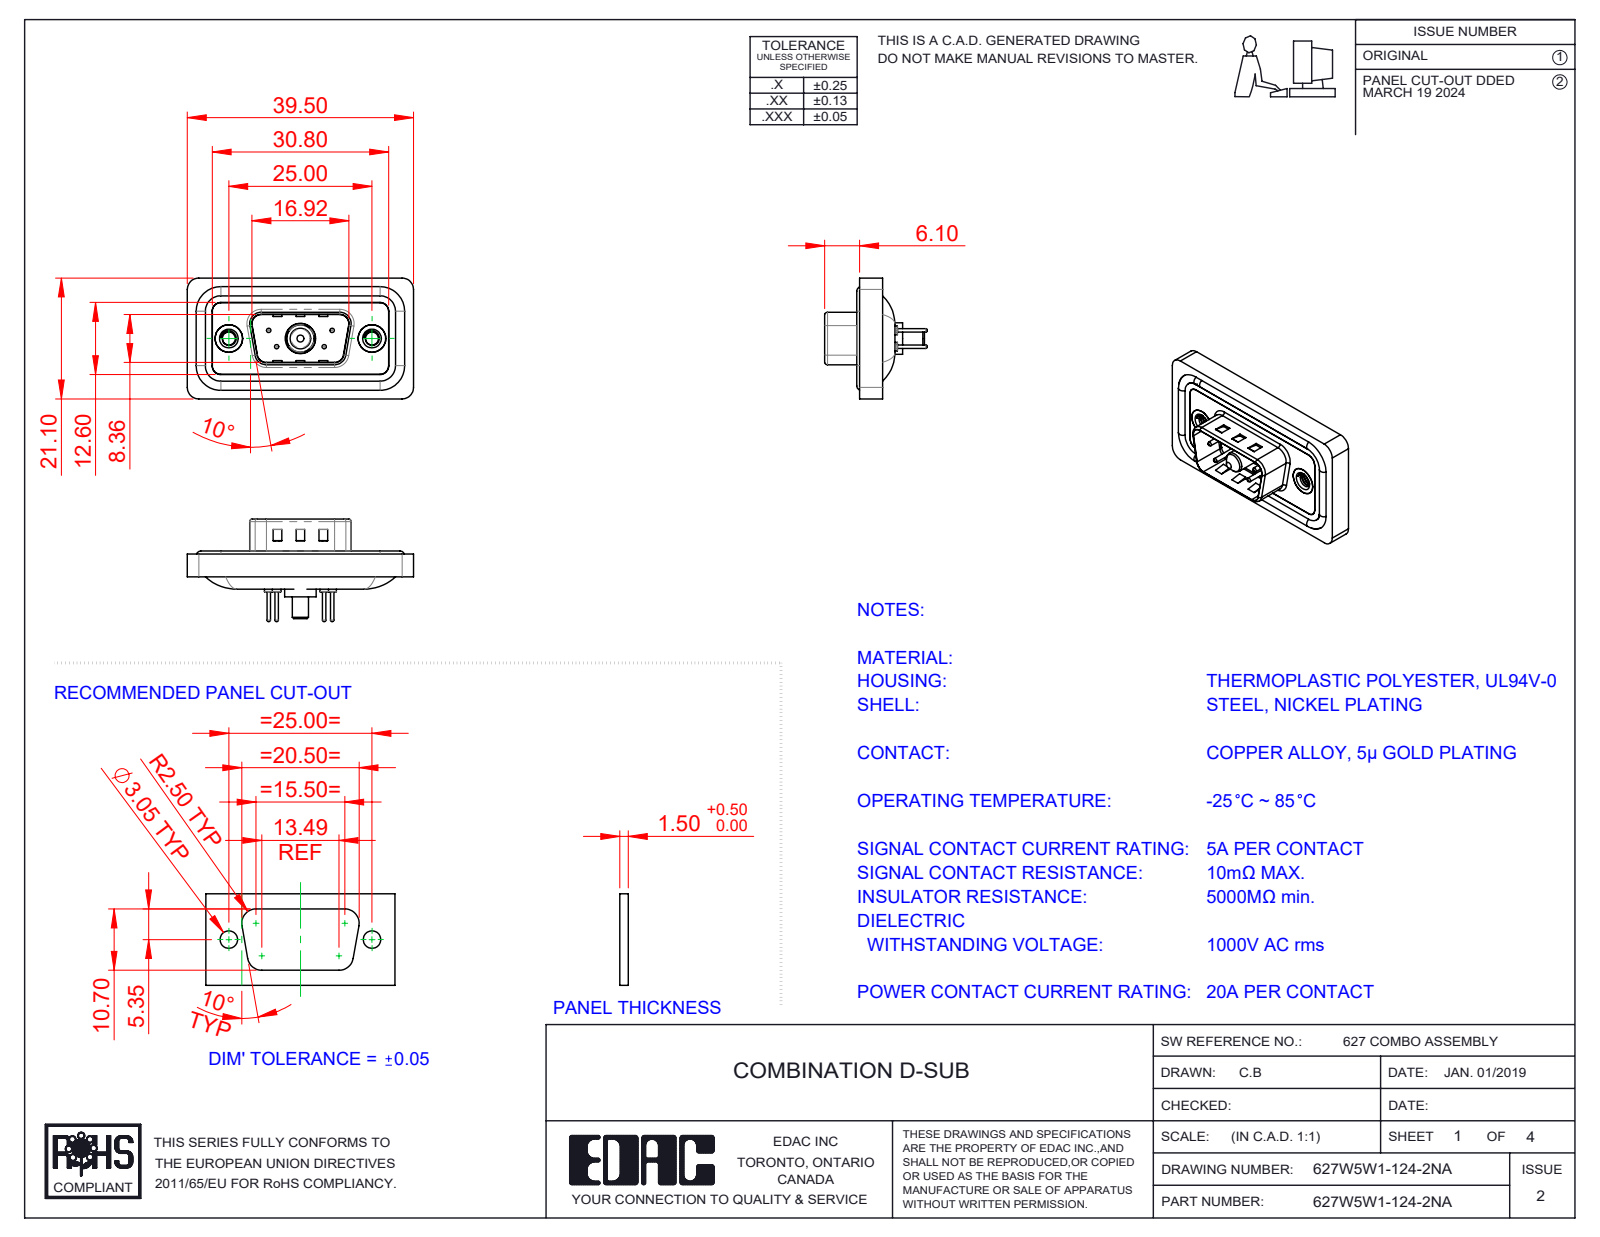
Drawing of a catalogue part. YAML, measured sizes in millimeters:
part_name: "627W5W1-124-2NA; 627Combo Contact Row 2_24; 627Combo Waterproof Housing_09 Contacts; 627Combo Threaded Rivet_A (+5 more)"
step_written_by: "SolidWorks 2023 (CONFIG_CONTROL_DESIGN)"
units: millimeters
bodies: {solids: 13, faces: 596, planar: 183, cylindrical: 257, other: 156}
overall_size: [39.5, 21.1, 17.9]
volume: 4389
surface_area: 6939
round_holes:
  - {diameter: 0.75, count: 4}
  - {diameter: 1.6, count: 4}
  - {diameter: 2, count: 4}
  - {diameter: 2.26, count: 2}
  - {diameter: 4, count: 2}
  - {diameter: 4.8, count: 2}
  - {diameter: 5, count: 2}
  - {diameter: 4.85, count: 1}
  - {diameter: 5.3, count: 1}
round_bosses_or_shafts:
  - {diameter: 1.6, count: 4}
  - {diameter: 1.5, count: 4}
  - {diameter: 0.6, count: 4}
  - {diameter: 4.9, count: 2}
  - {diameter: 5.5, count: 1}
  - {diameter: 5.2, count: 1}
  - {diameter: 4.75, count: 1}
  - {diameter: 3.75, count: 1}
partial_cylinders:
  - {radius: 1.5, count: 22}
  - {radius: 2, count: 18}
  - {radius: 0.5, count: 8}
  - {radius: 1.6, count: 8}
  - {radius: 0.25, count: 4}
  - {radius: 0.6, count: 4}
  - {radius: 0.65, count: 4}
  - {radius: 0.9, count: 4}
face_to_face_distances: [0.4, 1.1, 2.9, 1.6, 1.5, 3.1, 0.5, 2.5, 4, 0.8]
hole_center_spacings: [3.16, 5.72, 7.1, 12.5, 18.1, 4.39, 4.4, 8.31]
